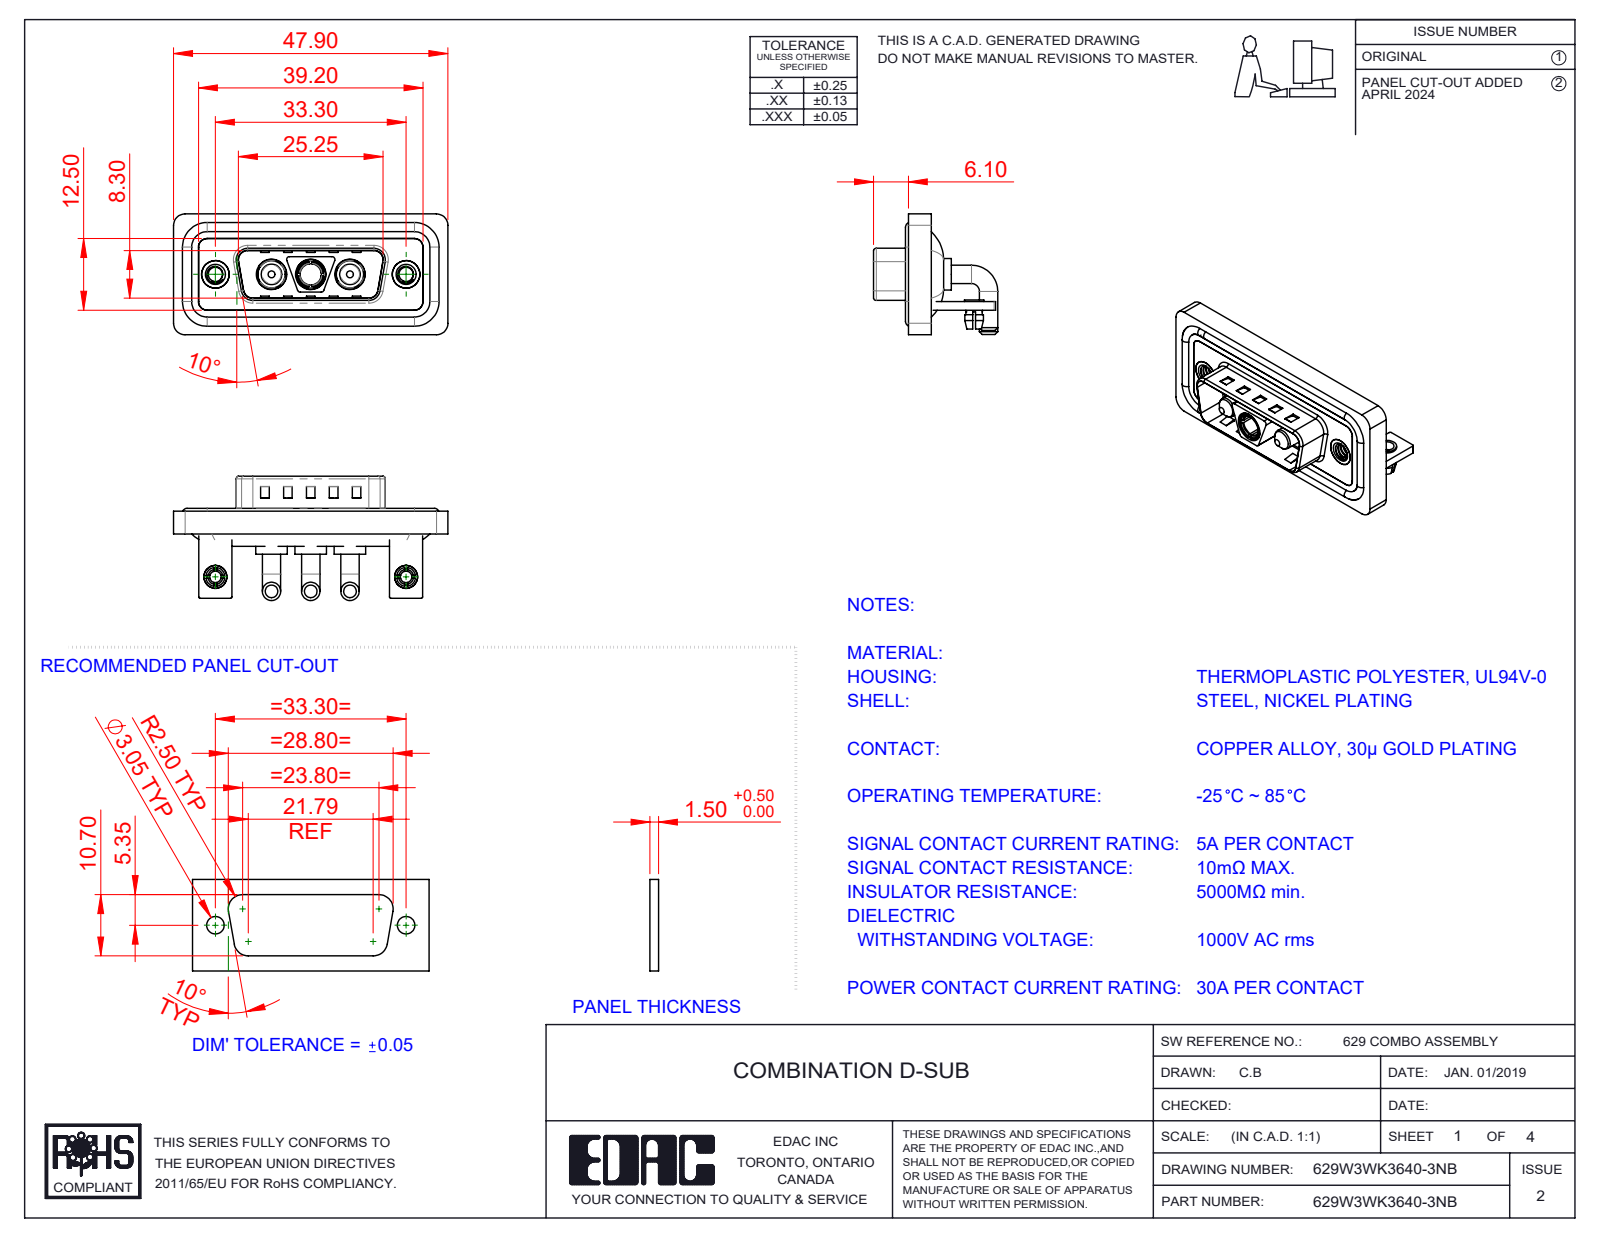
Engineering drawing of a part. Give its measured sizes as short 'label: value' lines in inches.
name: 629Combo Board Lock; 629Combo Housing_3WK3; 629Combo Waterproof Housing_15 Contacts; 629W3WK3640-3NB (+6 more)
written by: SolidWorks 2023 (CONFIG_CONTROL_DESIGN)
unit: in
bodies: 17 solids, 751 faces (299 planar, 306 cylindrical, 146 other)
size: 1.886 × 0.854 × 0.831
volume: 0.383 in³; area: 15.92 in²
holes: 4× ⌀0.098, 3× ⌀0.191, 3× ⌀0.209, 2× ⌀0.079, 2× ⌀0.126, 2× ⌀0.157, 2× ⌀0.189, 2× ⌀0.197, 1× ⌀0.146
bosses: 6× ⌀0.126, 4× ⌀0.063, 3× ⌀0.217, 3× ⌀0.205, 3× ⌀0.187, 3× ⌀0.148, 2× ⌀0.193, 2× ⌀0.157
rounds: 21× R0.079, 18× R0.059, 16× R0.01, 13× R0.02, 8× R0.063, 4× R0.024, 4× R0.026, 4× R0.035
face distances: 0.016, 0.059, 0.031, 0.114, 0.043, 0.083, 0.146, 0.063, 0.047, 0.177
hole spacings: 0.27, 0.386, 0.656, 0.925, 1.311, 0.539
